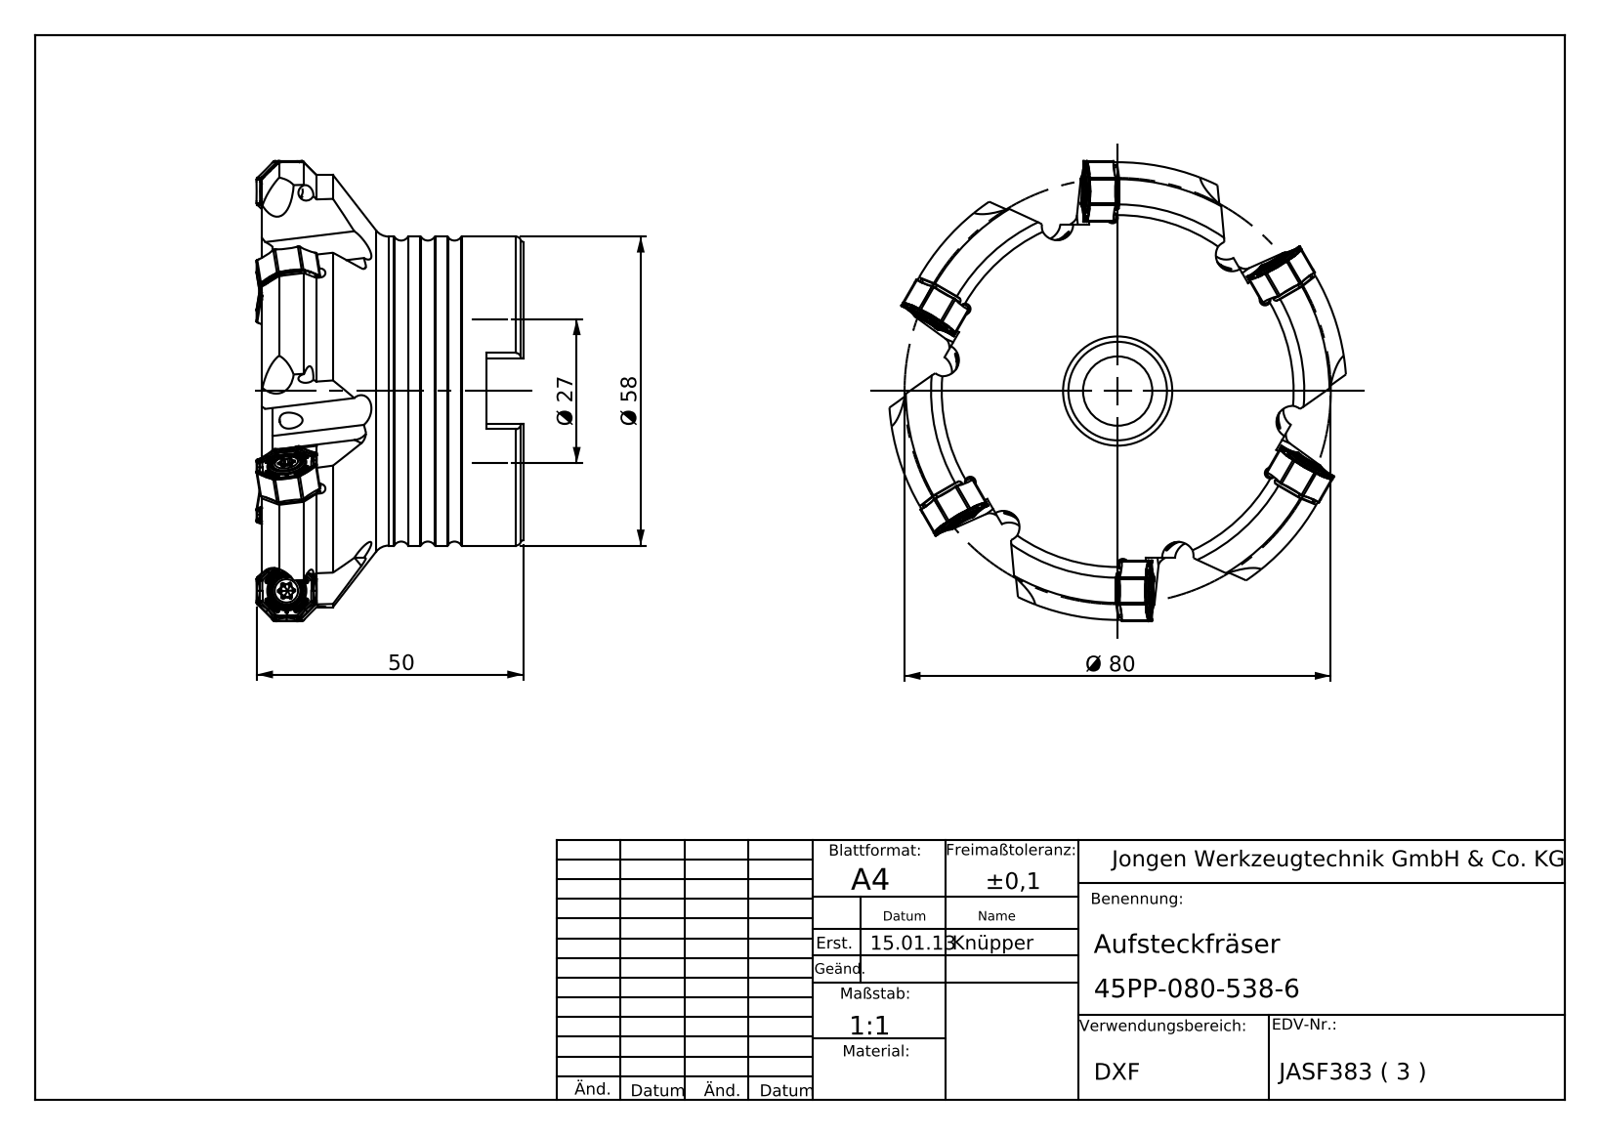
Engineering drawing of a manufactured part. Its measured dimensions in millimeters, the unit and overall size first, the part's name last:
Units: millimetres
Overall size (bounding box): 87.23 × 87.22 × 50.05
Round holes (diameter × count): ⌀3 ×6, ⌀13 ×1, ⌀18.5 ×1, ⌀26.95 ×1, ⌀27 ×1, ⌀27.15 ×1, ⌀27.3 ×1
Round bosses / shafts (diameter × count): ⌀58 ×1
Partial cylindrical surfaces — rounded edges, fillets, slot ends (radius × count): R1 ×18, R1.25 ×6, R3 ×6, R40.55 ×1
Main face-to-face distances: 47.1, 6.95, 40.15, 21.95, 15, 25.15, 12.4, 33.1, 26.15, 11.15
Volume: 147 770 mm³ · Surface area: 26 885 mm²
Bodies: 1 solid, 275 faces (92 planar, 92 cylindrical, 91 other)
Part name (STEP PRODUCT): 45PP-080-538-6
STEP written by: SolidWorks 2013 (AUTOMOTIVE_DESIGN)
